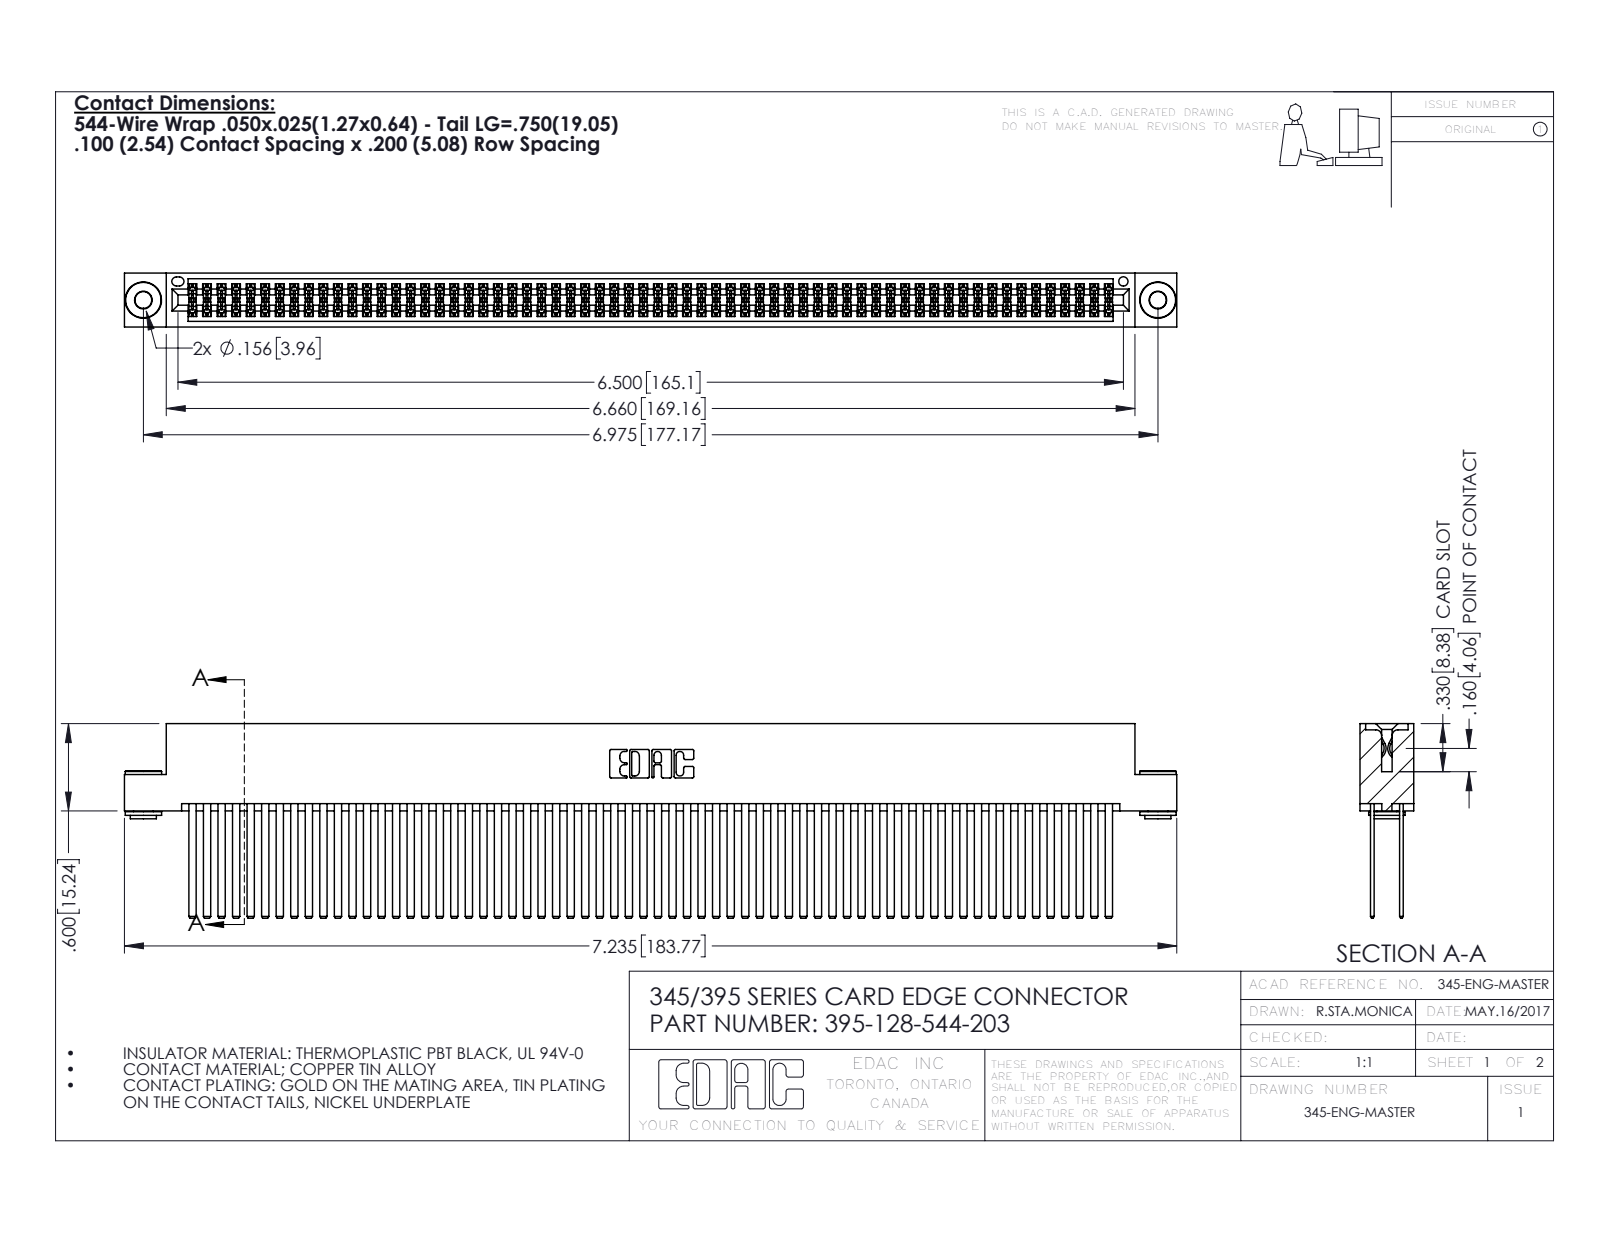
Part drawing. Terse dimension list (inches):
name: 345-292-001_345-293-144; 345 Part_Flush Mounting Lugs - 0.156 Dia-TH; 345-250-002_345-250-002-102; 395-128-544-203
written by: SolidWorks 2016 (CONFIG_CONTROL_DESIGN)
unit: in
bodies: 131 solids, 5796 faces (3802 planar, 1986 cylindrical, 8 other)
size: 7.235 × 1.337 × 0.37
volume: 1.213 in³; area: 54.65 in²
holes: 2× ⌀0.116, 2× ⌀0.156, 1× ⌀0.064
bosses: 2× ⌀0.25, 2× ⌀0.18, 2× ⌀0.136
rounds: 192× R0.006, 22× R0.01, 6× R0.007, 6× R0.031, 3× R0.026, 2× R0.014, 2× R0.019, 2× R0.022
face distances: 0.2, 0.025, 0.072, 0.098, 0.272, 0.298, 0.225, 0.175, 0.37, 0.05
hole spacings: 0.27, 6.739, 6.975
